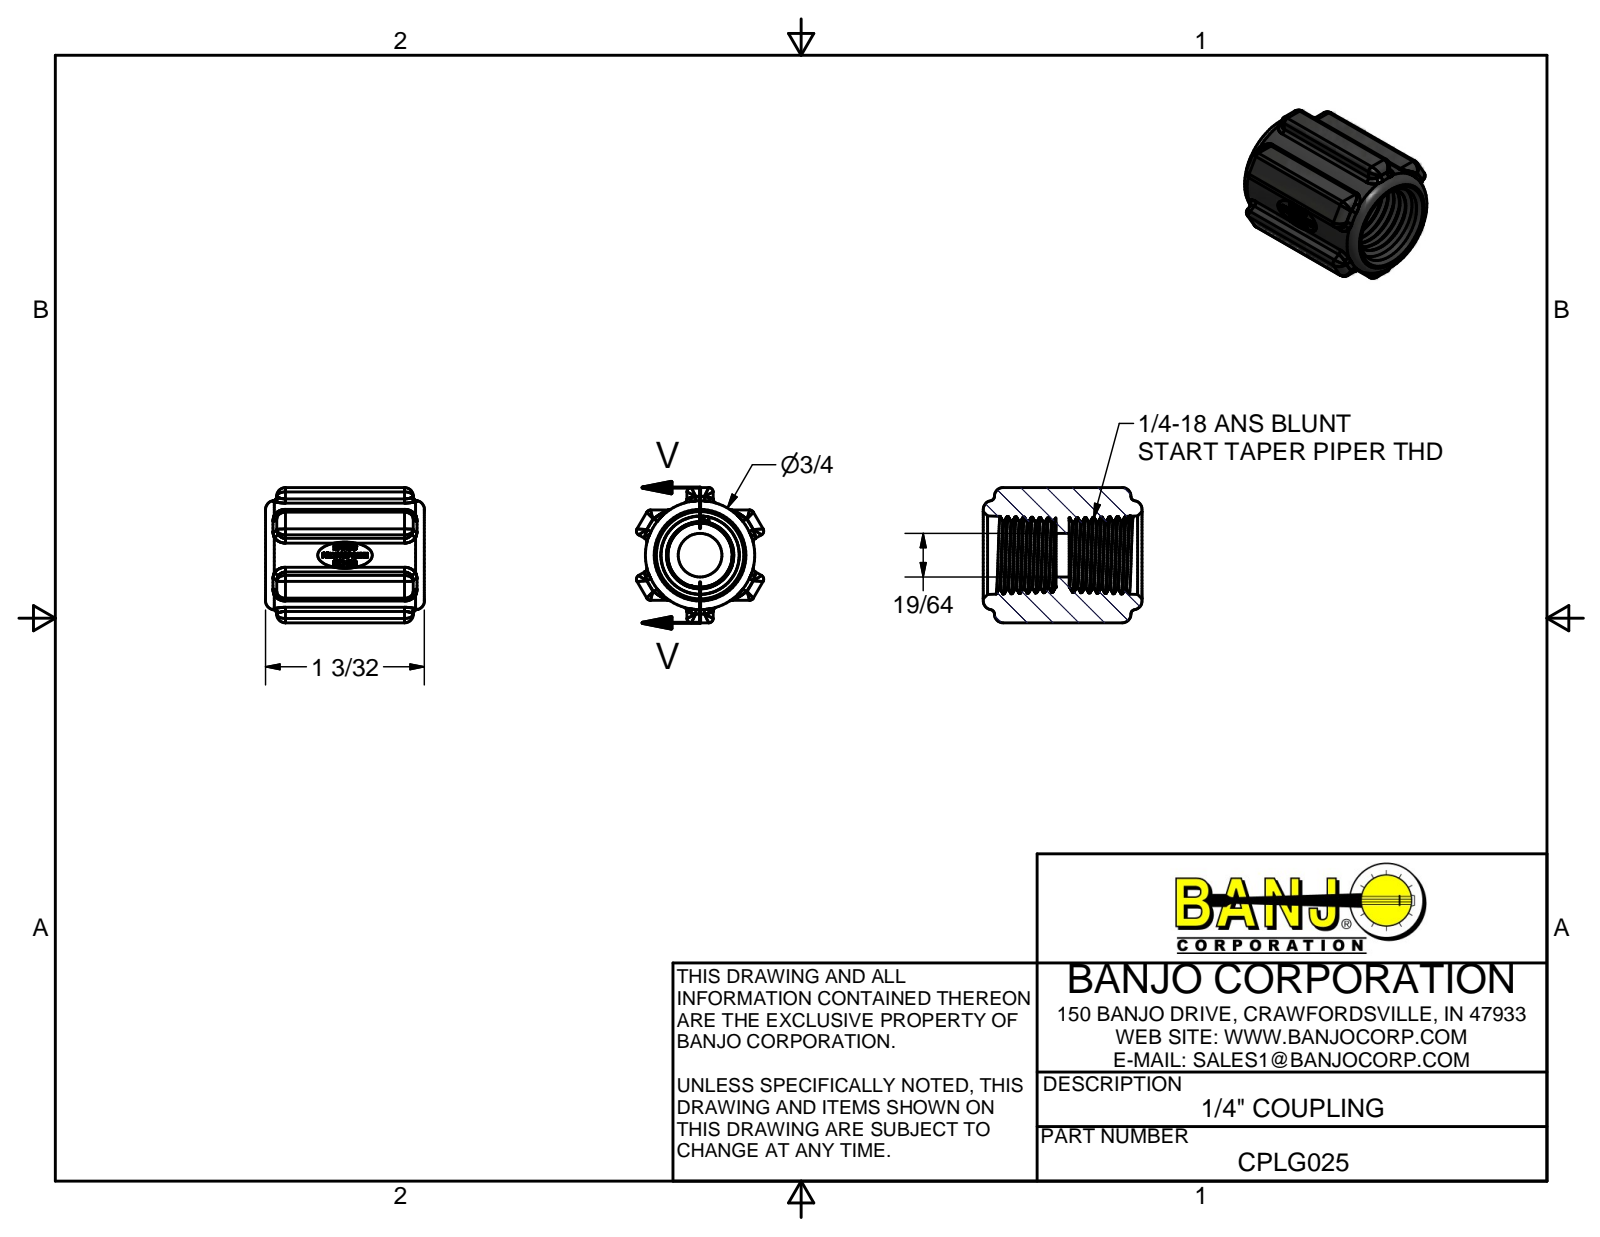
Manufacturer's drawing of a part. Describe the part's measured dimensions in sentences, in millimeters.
The part is named "CPLG025". Its 3-D file was written by "Autodesk Inventor 2014 (AUTOMOTIVE_DESIGN)". It is 1 solid with 572 faces: 195 planar, 105 cylindrical and 272 other. Overall it measures 27.69 by 23.62 by 22.18 millimeters. Its volume is 6 216 cubic millimeters and its surface area 4 270 square millimeters. Round holes: 1 of diameter 7.62. Partial cylindrical surfaces (rounded edges, fillets, slot ends): 28 of radius 1.52, 24 of radius 0.76, 1 of radius 9.27, 1 of radius 9.53. The main face-to-face distances are 23.62, 15.78, 3.92, 19.7, 4.58, 2.28, 12.7, 14.98, 27.68, 13.05.
